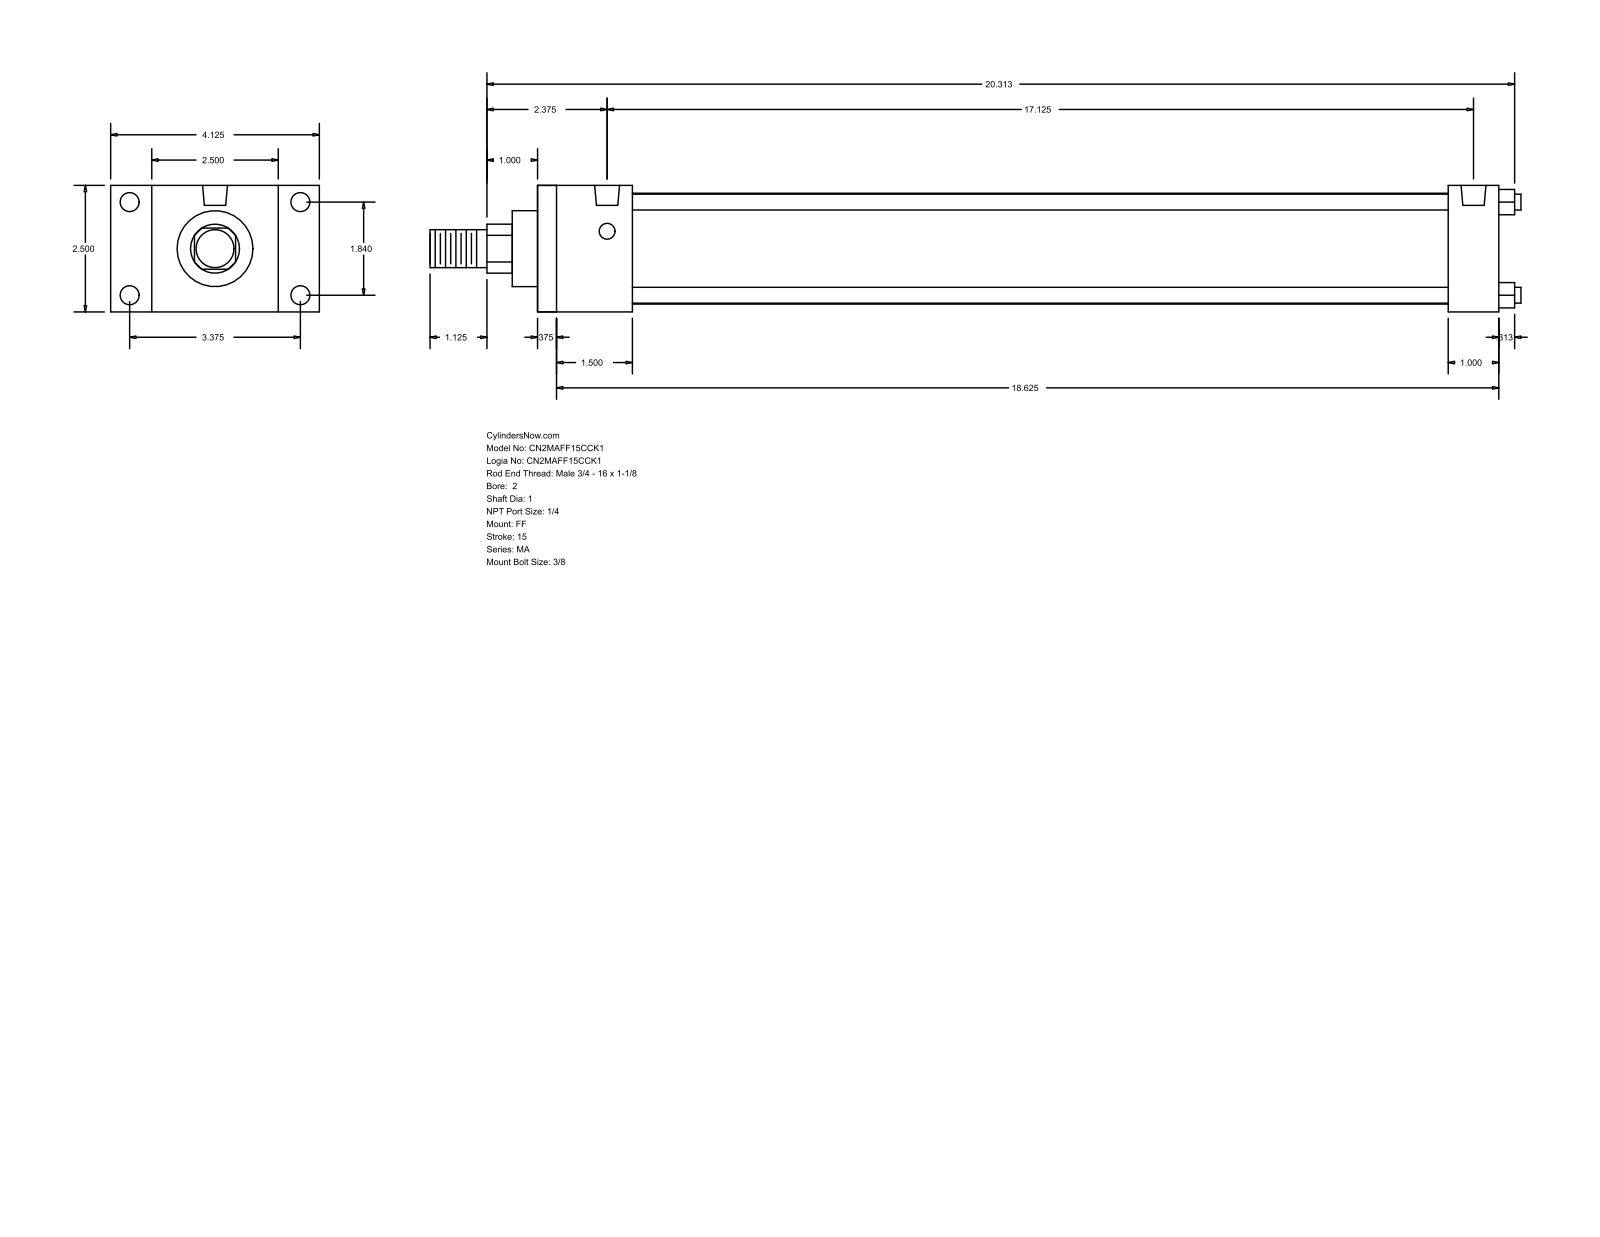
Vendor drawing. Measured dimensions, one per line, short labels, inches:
name: MA_FF__0200_1
written by: GSSL Pune (CONFIG_CONTROL_DESIGN)
unit: in
bodies: 0 solids, 92 faces (64 planar, 28 cylindrical, 0 other)
size: 21.563 × 4.125 × 2.5
holes: 4× ⌀0.313, 4× ⌀0.375, 2× ⌀0.492
bosses: 4× ⌀0.313, 1× ⌀2.19, 1× ⌀1.5, 1× ⌀1, 1× ⌀0.75
rounds: 1× R0.484
face distances: 2.5, 19, 0.375, 18.625, 1, 0.813, 0.5, 1.875, 18, 1.5
hole spacings: 1.84, 3.375, 3.844, 17.125
